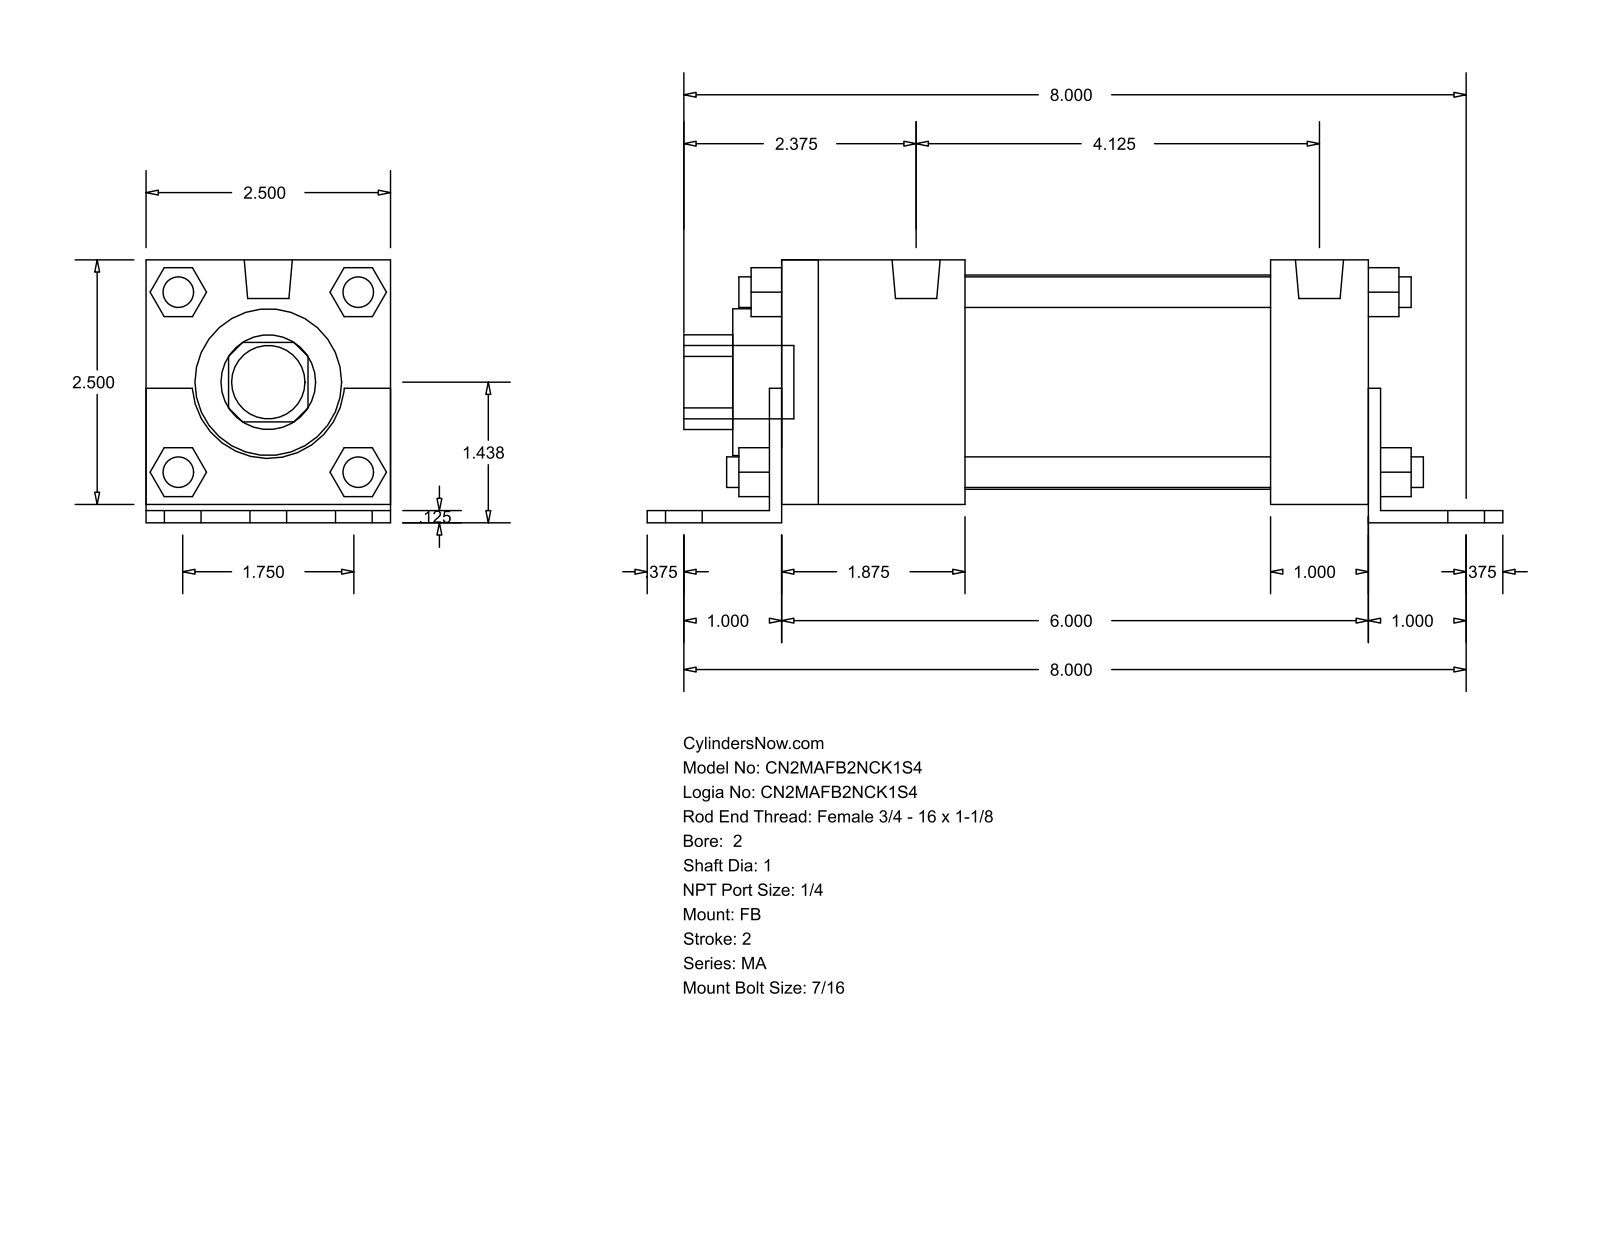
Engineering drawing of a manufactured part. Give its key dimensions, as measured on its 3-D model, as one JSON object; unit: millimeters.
{"part_name": "MA_FB__0200_1", "step_written_by": "GSSL Pune (CONFIG_CONTROL_DESIGN)", "units": "millimeters", "bodies": {"solids": 0, "faces": 140, "planar": 105, "cylindrical": 35, "other": 0}, "overall_size": [222.25, 68.26, 63.5], "round_holes": [[25.4, 1], [38.1, 1], [55.63, 1]], "round_bosses_or_shafts": [[7.94, 8], [11.11, 6], [12.49, 2], [19.05, 1]], "partial_cylinders_radius": [[12.29, 1], [19.81, 1]], "face_to_face_distances": [63.5, 3.17, 4.76, 68.26, 1.59, 65.09, 155.57, 12.7, 152.4, 25.4]}
